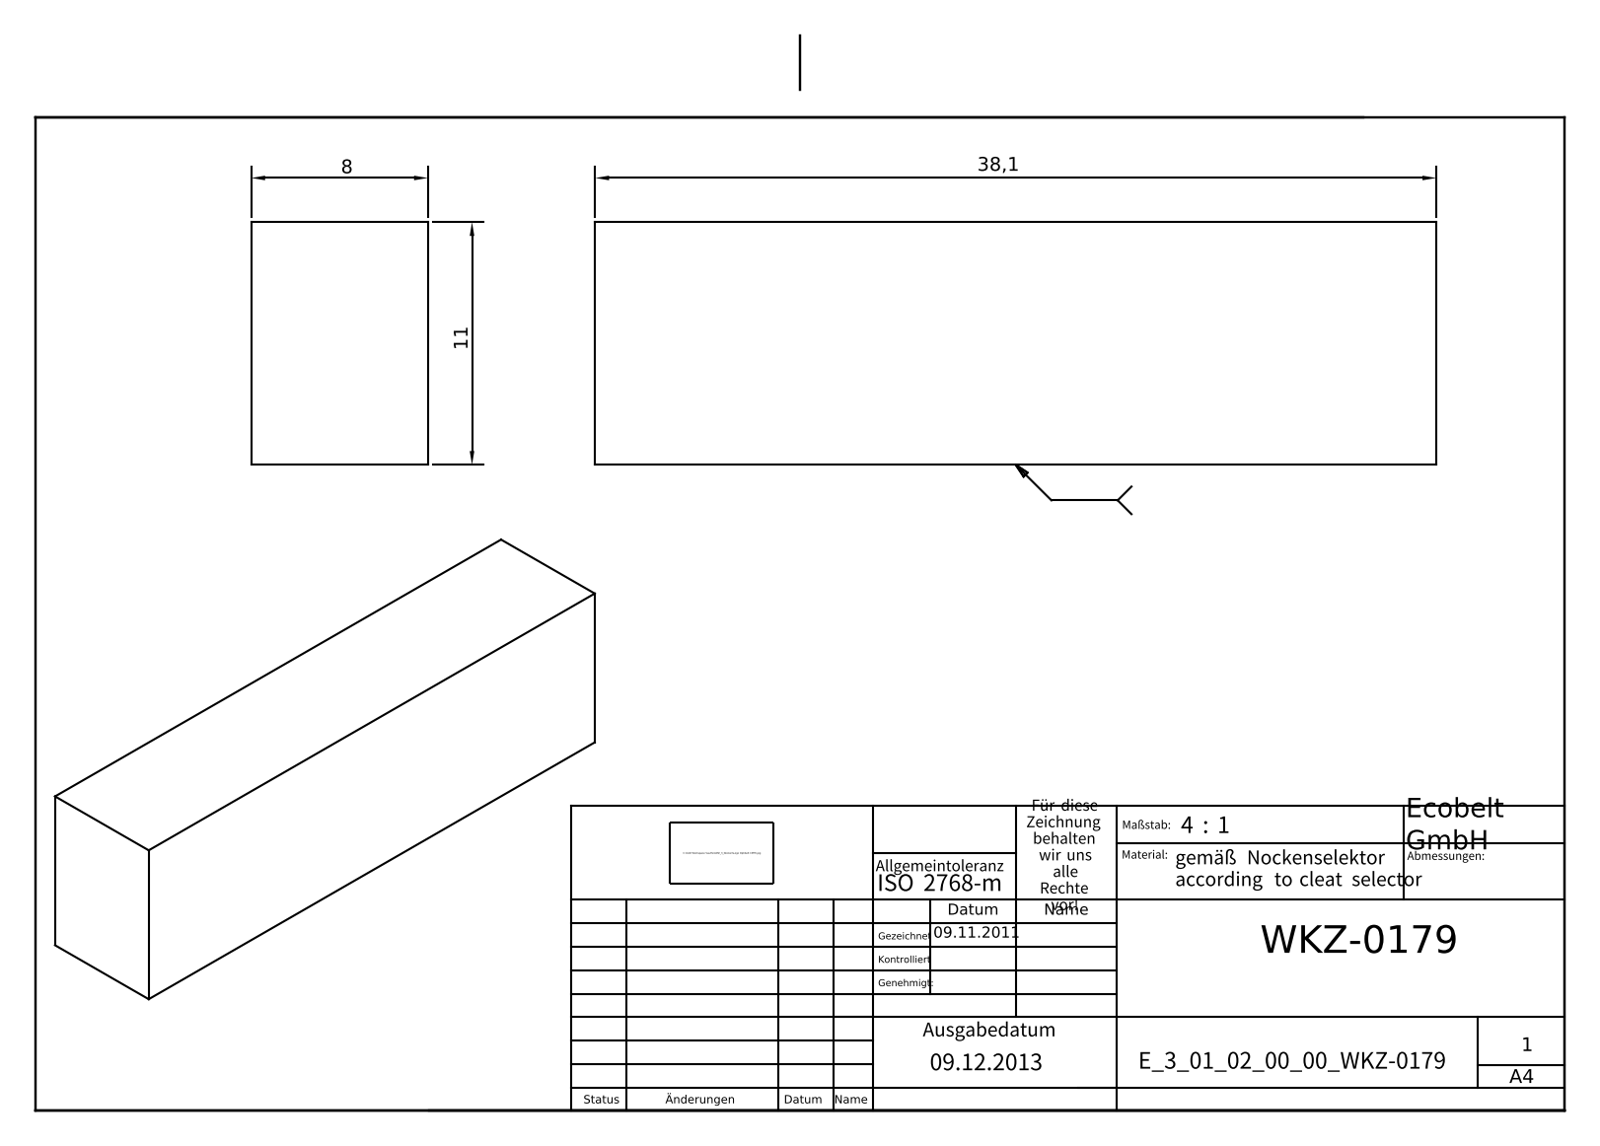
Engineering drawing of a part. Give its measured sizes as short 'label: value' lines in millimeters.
name: E_3_01_02_00_00_WKZ-0179
written by: Autodesk Inventor 2021 (AUTOMOTIVE_DESIGN)
unit: mm
bodies: 1 solid, 6 faces (6 planar, 0 cylindrical, 0 other)
size: 38.1 × 11 × 8
volume: 3 353 mm³; area: 1 624 mm²
face distances: 8, 11, 38.1
